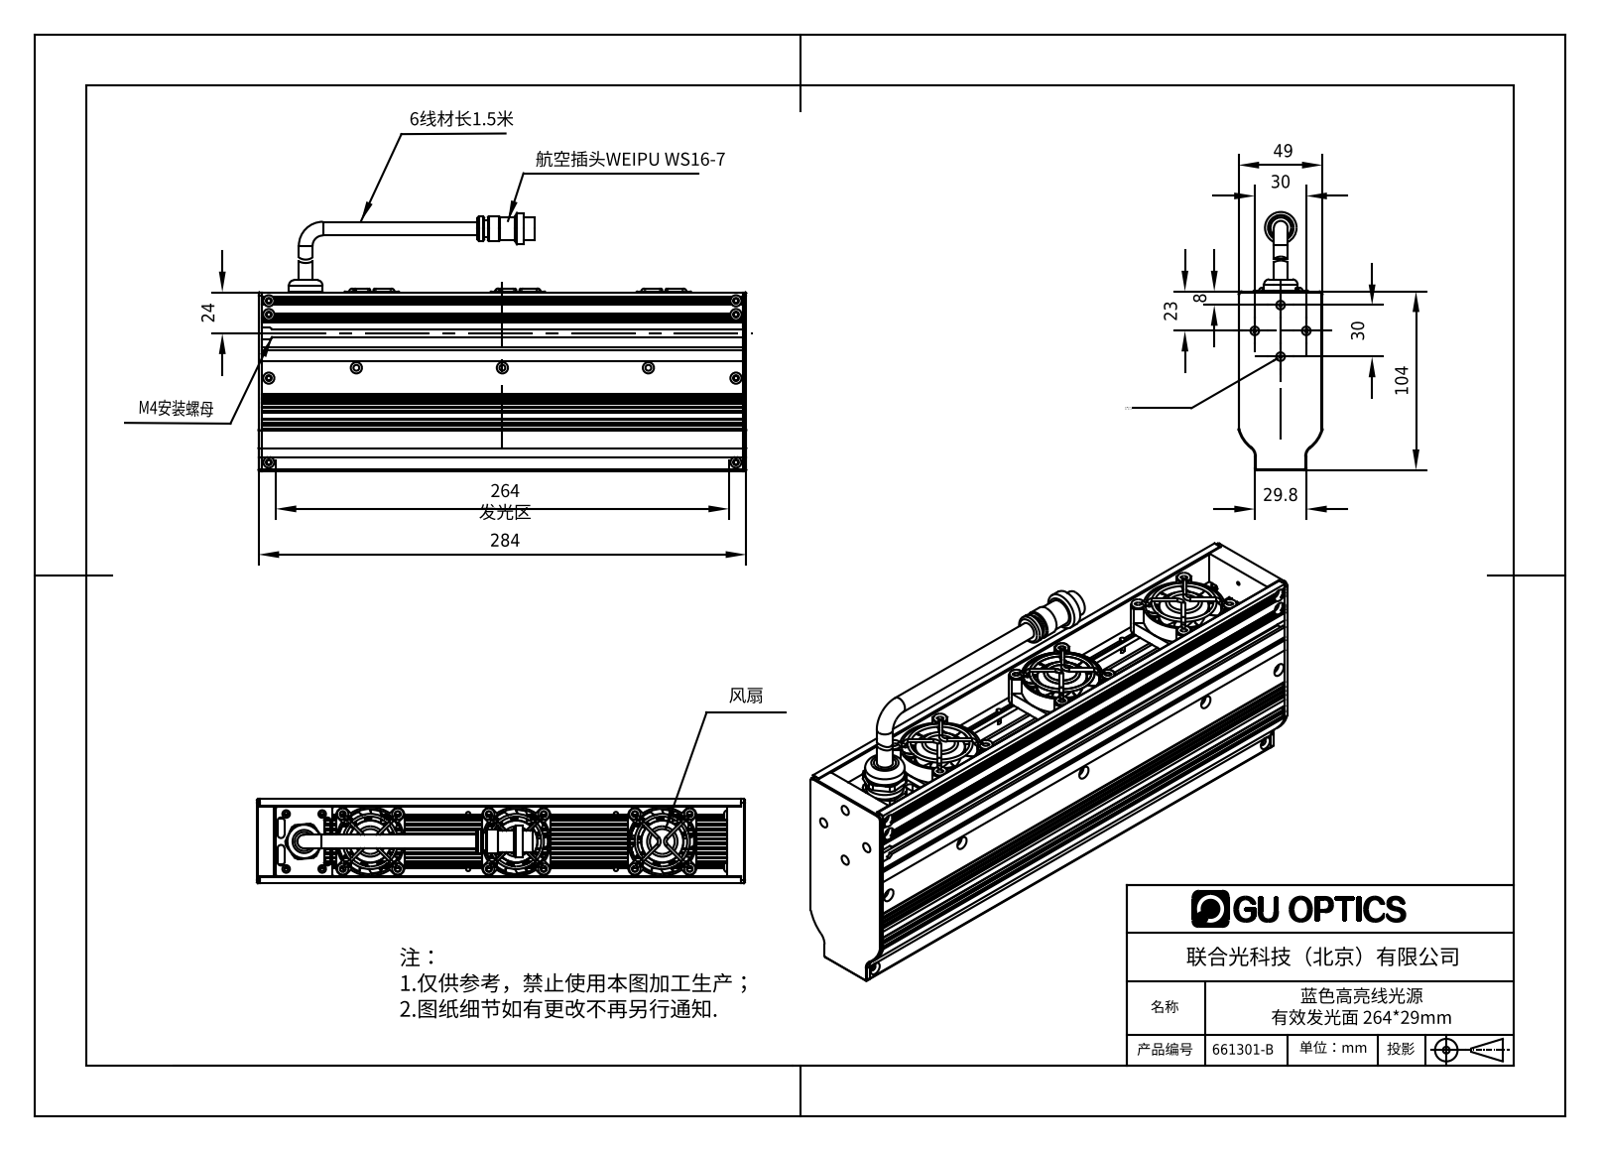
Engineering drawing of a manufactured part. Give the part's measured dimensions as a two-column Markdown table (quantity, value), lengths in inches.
| quantity | value |
| --- | --- |
| part name | 661301-B |
| STEP written by | SolidWorks 2016 (AUTOMOTIVE_DESIGN) |
| units | inches |
| bodies | 31 solids, 2506 faces (981 planar, 776 cylindrical, 749 other) |
| overall size | 11.181 × 5.913 × 1.929 |
| volume | 48.87 in³ |
| surface area | 587.9 in² |
| round holes (diameter × count) | 0.098 × 25, 0.126 × 12, 0.244 × 12, 0.134 × 11, 0.063 × 10, 0.138 × 10, 0.256 × 9, 0.039 × 6, 0.094 × 4, 0.197 × 4, 1.496 × 3, 0.433 × 1 |
| round bosses / shafts (diameter × count) | 0.063 × 12, 0.976 × 3, 0.945 × 3, 0.079 × 3, 0.315 × 2, 1.378 × 1, 0.768 × 1, 0.748 × 1 |
| partial cylindrical surfaces (radius × count) | 0.039 × 58, 0.008 × 28, 0.079 × 20, 0.201 × 13, 0.016 × 12, 0.02 × 10, 0.118 × 7, 0.044 × 6 |
| main face-to-face distances | 0.079, 0.217, 0.197, 0.433, 0.201, 1.728, 0.15, 0.067, 1.925, 1.724 |
| hole center spacings | 1.26, 0.138, 3.346, 3.386, 1.253, 1.772, 1.055, 0.138 |
